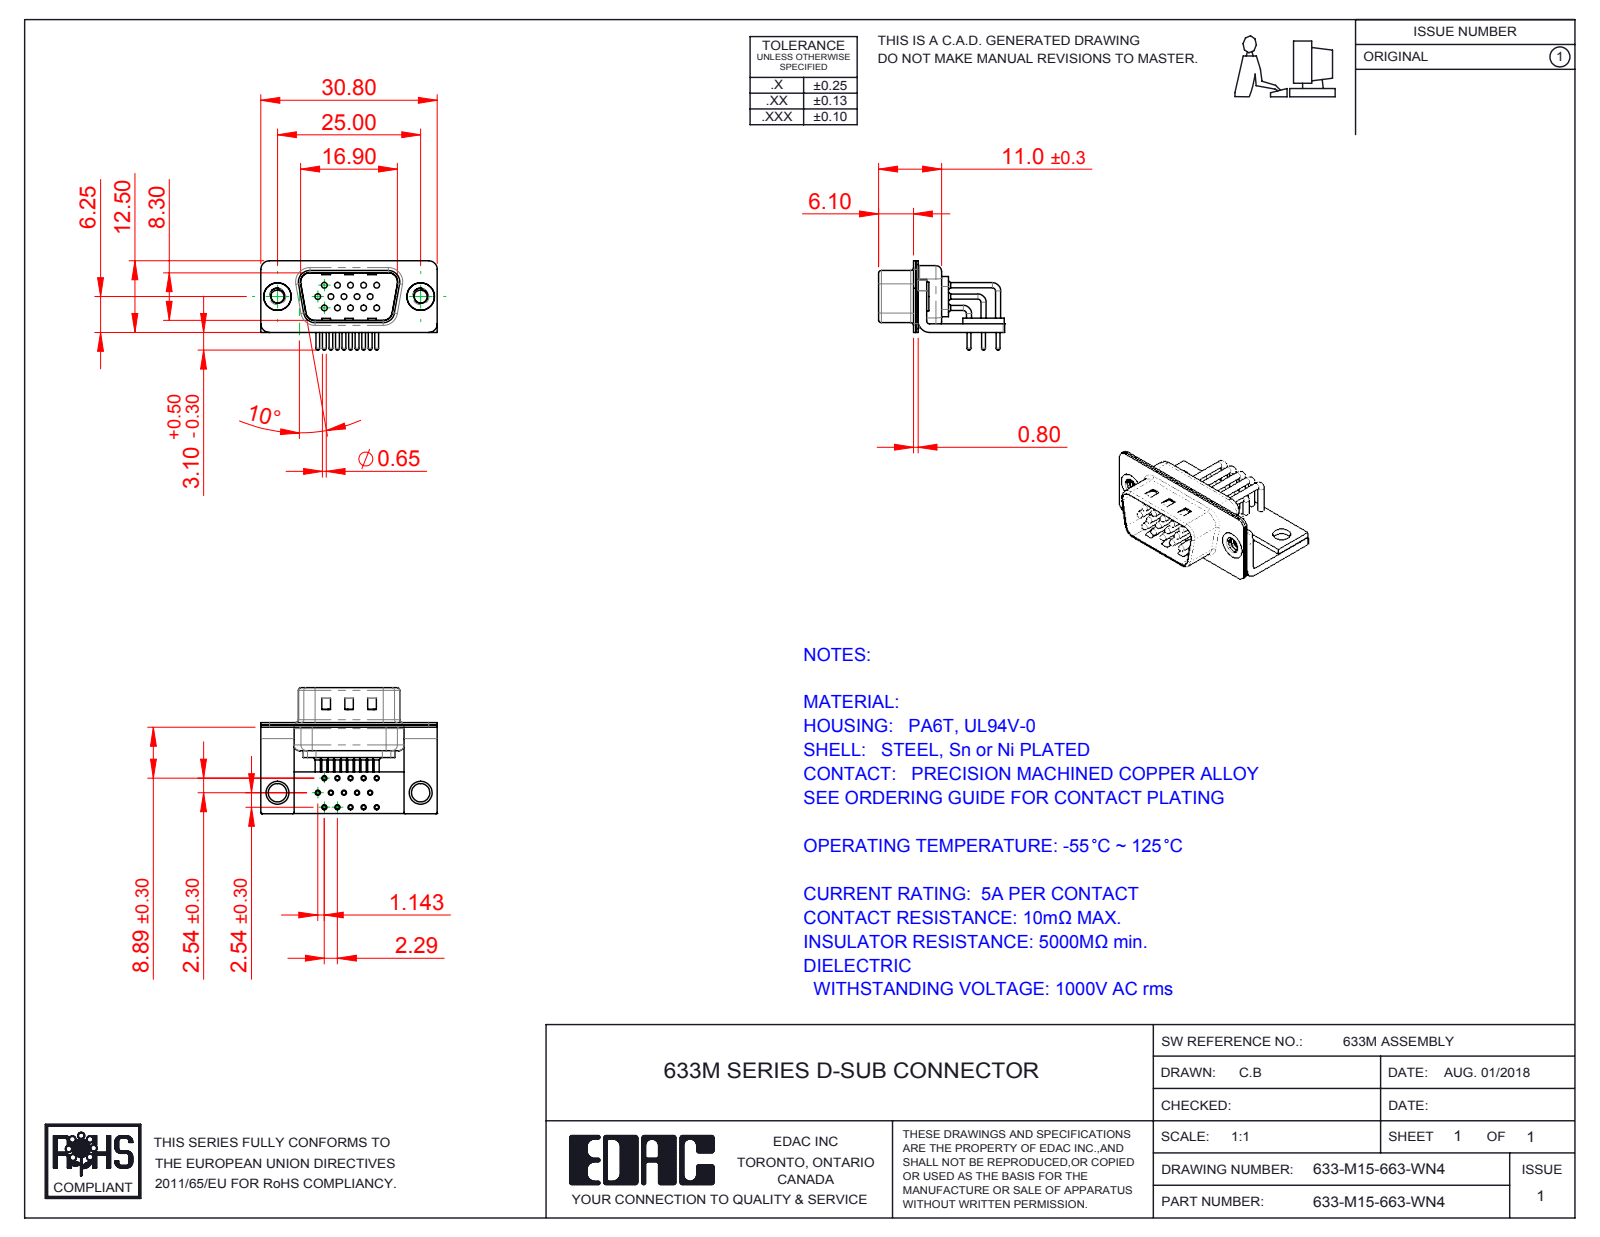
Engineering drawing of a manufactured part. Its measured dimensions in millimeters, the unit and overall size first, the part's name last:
Units: millimetres
Overall size (bounding box): 30.8 × 22 × 15.6
Round holes (diameter × count): ⌀0.9 ×15, ⌀1 ×15, ⌀1.7 ×15, ⌀2 ×15, ⌀2.26 ×2, ⌀3.2 ×2, ⌀4 ×2, ⌀4.8 ×2
Round bosses / shafts (diameter × count): ⌀0.9 ×16, ⌀1.5 ×15, ⌀0.65 ×15, ⌀5 ×2, ⌀4.9 ×2
Partial cylindrical surfaces — rounded edges, fillets, slot ends (radius × count): R0.25 ×16, R1.5 ×16, R1.01 ×15, R2 ×13, R0.5 ×9, R1.6 ×8, R0.6 ×4, R0.65 ×4
Main face-to-face distances: 0.4, 1.5, 0.8, 1, 0.85, 1.9, 1.25, 2.5, 10.4, 9.55
Hole centre spacings: 2.29, 4.57, 2.28, 3.96, 2.78, 4.27, 6.05, 6.86
Volume: 1 926 mm³ · Surface area: 5 768 mm²
Bodies: 23 solids, 2034 faces (1093 planar, 721 cylindrical, 220 other)
Part name (STEP PRODUCT): 633M Stabilizer Board_15 Contacts; 633M Shell Rear_15 Contacts; 633M 4-40 Threaded Rivet_Stabilizer; 633M Contact Row 1 (+6 more)
STEP written by: SolidWorks 2016 (CONFIG_CONTROL_DESIGN)
